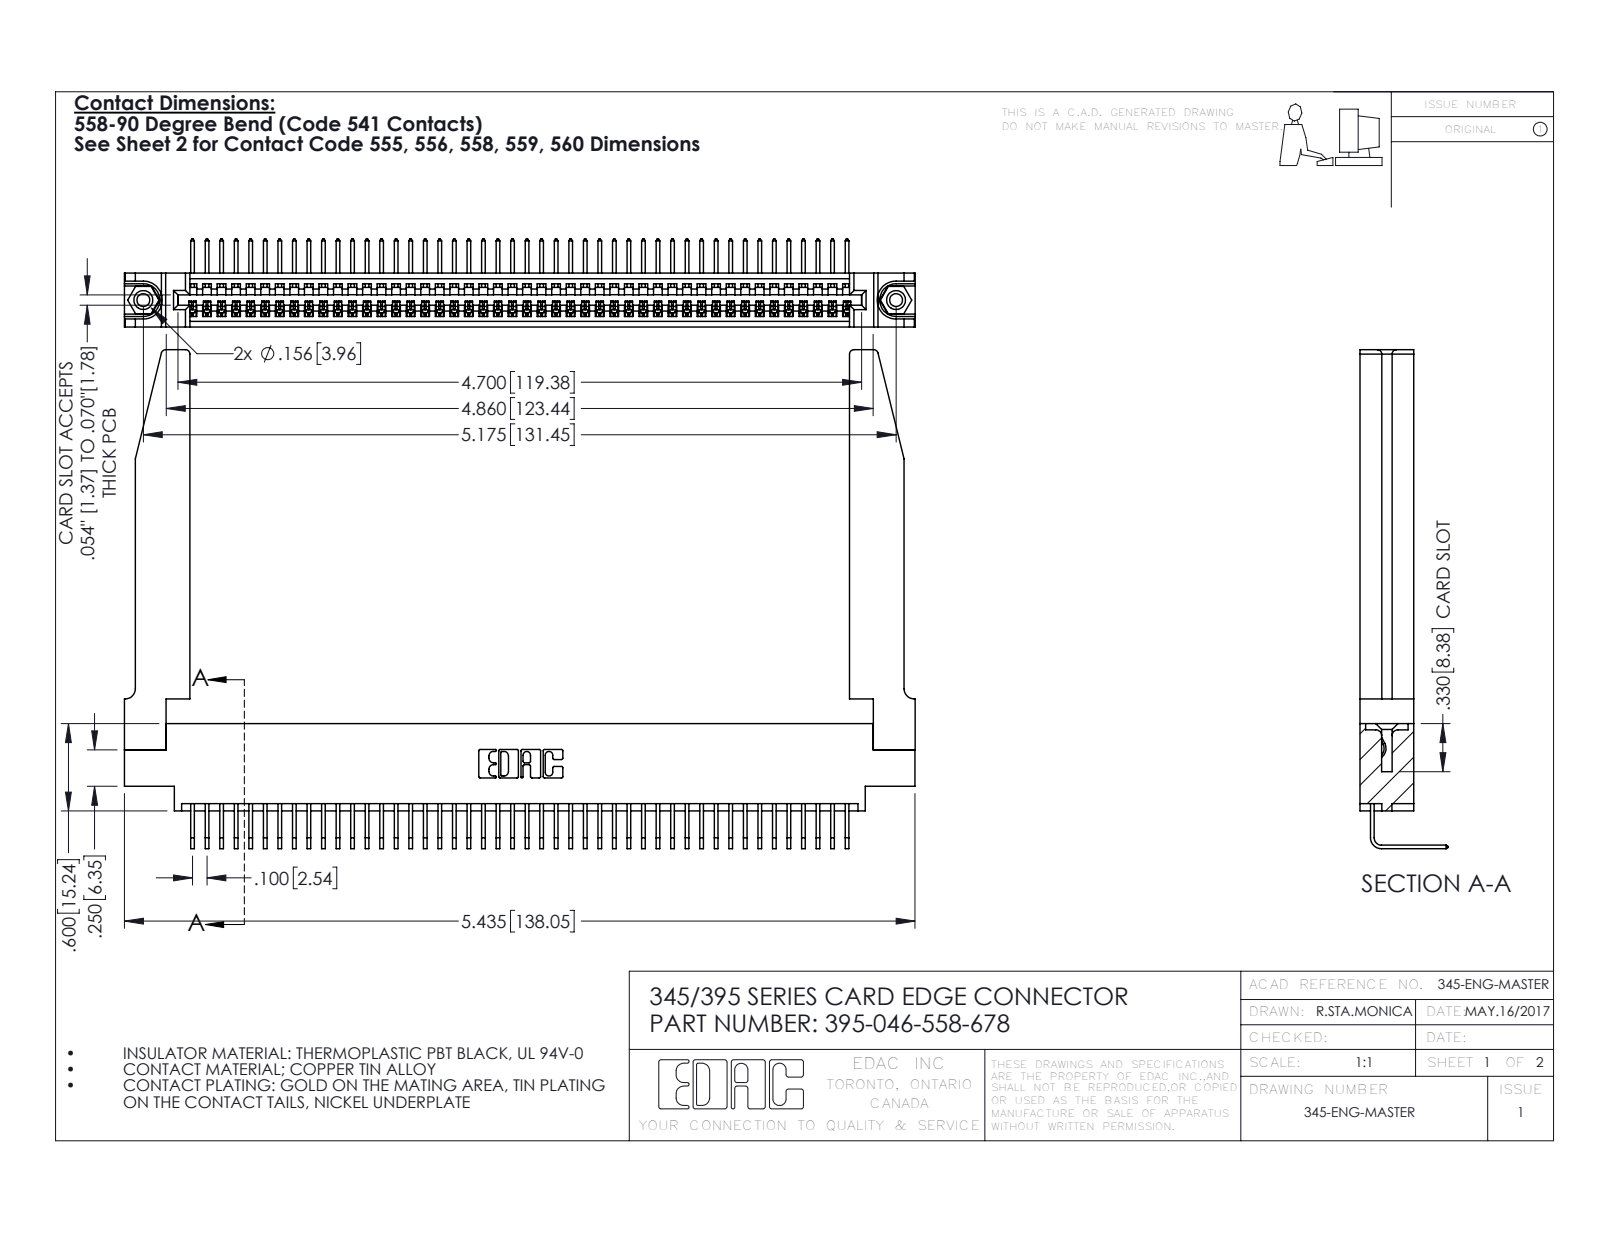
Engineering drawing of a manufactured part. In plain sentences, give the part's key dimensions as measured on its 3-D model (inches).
The part is named "345 Part_0.170 Offset - 0.156 Dia-TH; 345-220-078_345-220-078; 345-292-001_558 Tail - 2; 395-046-558-678 (+1 more)". Its 3-D file was written by "SolidWorks 2016 (CONFIG_CONTROL_DESIGN)". It is 51 solids with 3124 faces: 2158 planar, 914 cylindrical and 52 other. Overall it measures 5.436 by 3.429 by 0.605 inches. Its volume is 1.279 cubic inches and its surface area 39.45 square inches. Round holes: 2 of diameter 0.089, 2 of diameter 0.125, 2 of diameter 0.156, 1 of diameter 0.064. Round bosses or shafts: 2 of diameter 0.155. Partial cylindrical surfaces (rounded edges, fillets, slot ends): 92 of radius 0.006, 22 of radius 0.01, 8 of radius 0.03, 6 of radius 0.007, 6 of radius 0.031, 3 of radius 0.026, 2 of radius 0.031, 2 of radius 0.04. The main face-to-face distances are 0.37, 0.072, 0.298, 0.2, 0.098, 0.272, 0.025, 0.225, 0.148, 0.15. The hole center spacings are 0.27, 4.939, 5.175.
